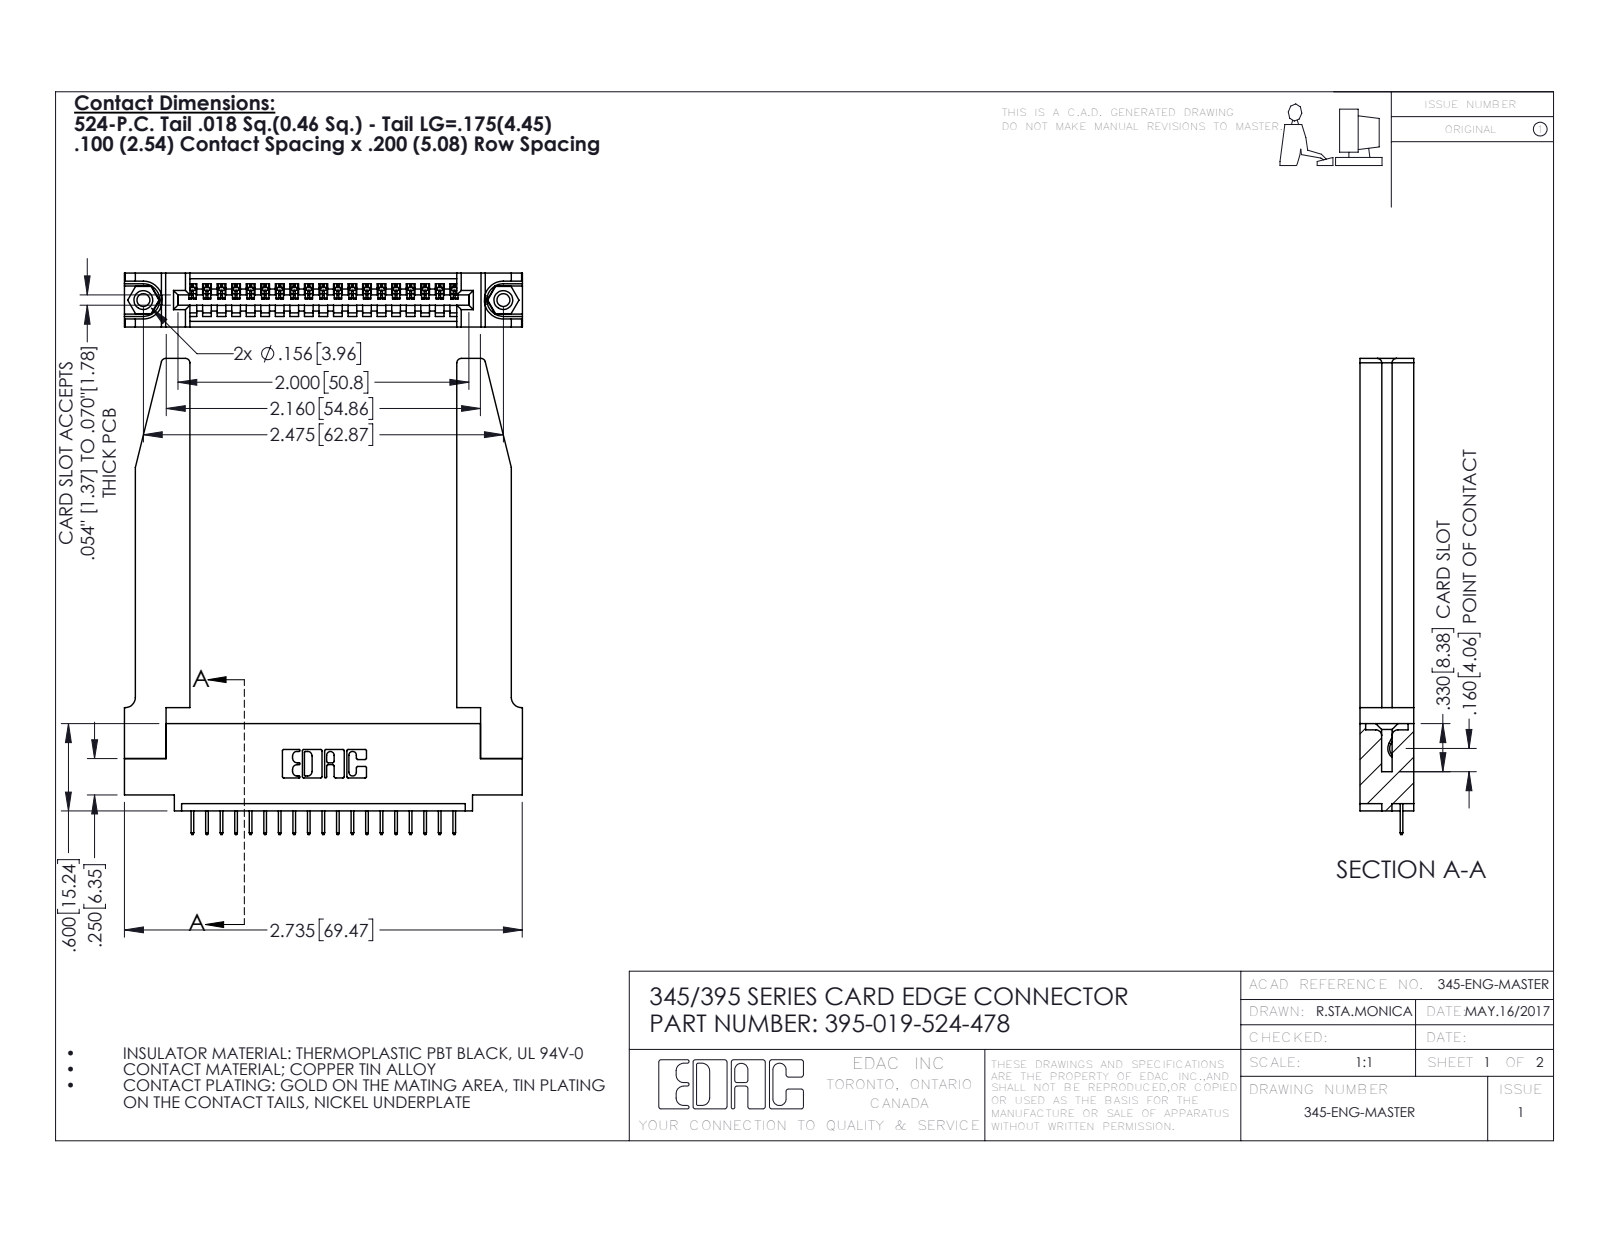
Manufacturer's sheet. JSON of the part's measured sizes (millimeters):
{"part_name": "345-292-001_345-293-124; 345 Part_0.110 Offset - 0.156 Dia-TH; 395-019-524-478; 345-220-078_345-220-078 (+1 more)", "step_written_by": "SolidWorks 2016 (CONFIG_CONTROL_DESIGN)", "units": "millimeters", "bodies": {"solids": 24, "faces": 1542, "planar": 1100, "cylindrical": 390, "other": 52}, "overall_size": [83.1, 69.5, 9.4], "volume_mm3": 14000, "surface_area_mm2": 14700, "round_holes": [[2.3, 2], [3.2, 2], [4, 2], [1.6, 1]], "round_bosses_or_shafts": [[3.9, 2]], "partial_cylinders_radius": [[0.2, 38], [0.3, 22], [0.8, 8], [0.2, 6], [0.8, 6], [0.7, 3], [0.8, 2], [1, 2]], "face_to_face_distances": [9.4, 1.8, 7.6, 3.8, 3.8, 5.1, 2.5, 6.9, 0.6, 5.6], "hole_center_spacings": [6.9, 56.9, 62.9]}
